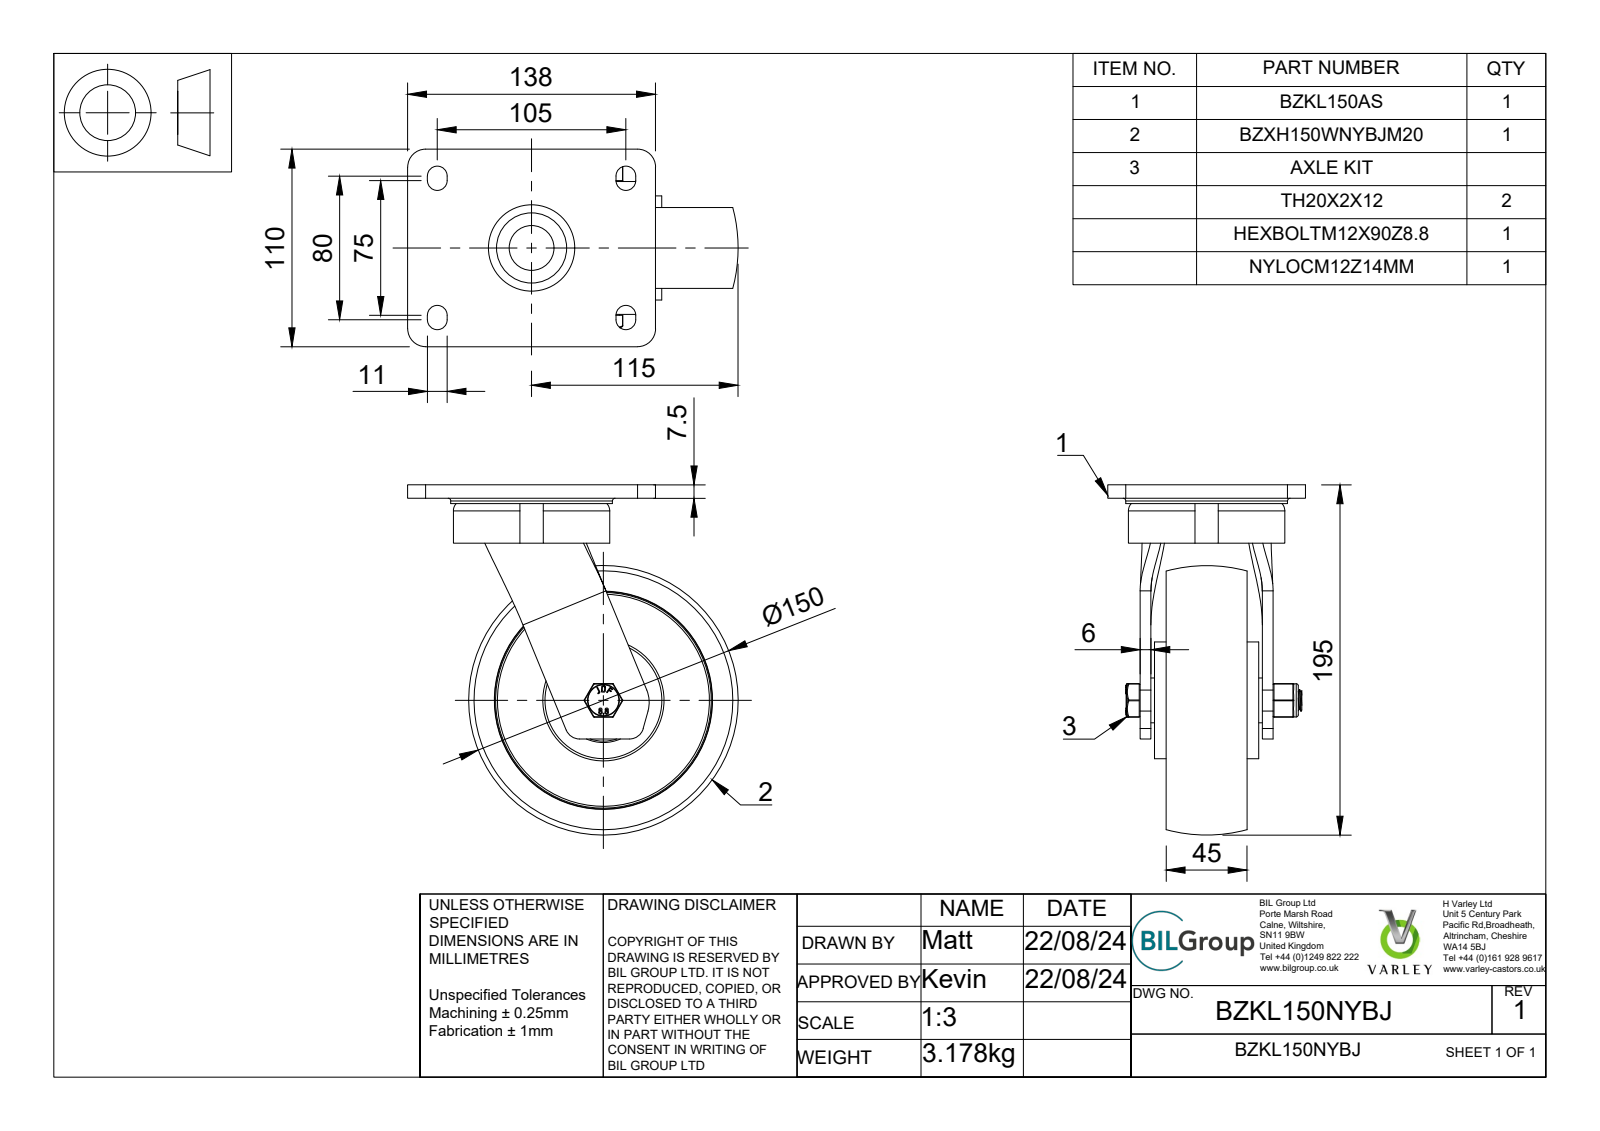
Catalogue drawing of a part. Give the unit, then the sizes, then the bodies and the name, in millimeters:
Units: millimetres
Overall size (bounding box): 195 × 184 × 110
Round holes (diameter × count): ⌀12 ×1, ⌀12.2 ×1, ⌀13 ×1, ⌀14 ×1, ⌀20 ×1, ⌀21.5 ×1, ⌀28.5 ×1, ⌀30.8 ×1, ⌀40.3 ×1, ⌀40.5 ×1, ⌀42 ×1, ⌀47 ×1
Round bosses / shafts (diameter × count): ⌀90 ×1, ⌀88 ×1, ⌀65 ×1, ⌀40.8 ×1, ⌀31.3 ×1, ⌀27 ×1, ⌀25.4 ×1, ⌀25 ×1
Partial cylindrical surfaces — rounded edges, fillets, slot ends (radius × count): R0.5 ×19, R5.5 ×8, R1 ×6, R0.47 ×4, R0.9 ×4, R10 ×4, R0.89 ×2, R0.89 ×2
Main face-to-face distances: 7.5, 25, 8.5, 16.5, 6, 28.5, 59.5, 53.5, 31, 37
Volume: 819 436 mm³ · Surface area: 211 905 mm²
Bodies: 35 solids, 1048 faces (418 planar, 209 cylindrical, 421 other)
Part name (STEP PRODUCT): BZKL150NYBJ v3; BZXH150WNYBJM20 v1; BEARING6204; BEARING62042 (+7 more)
STEP written by: Autodesk Translation Framework v13.14.0.145 (AUTOMOTIVE_DESIGN)
